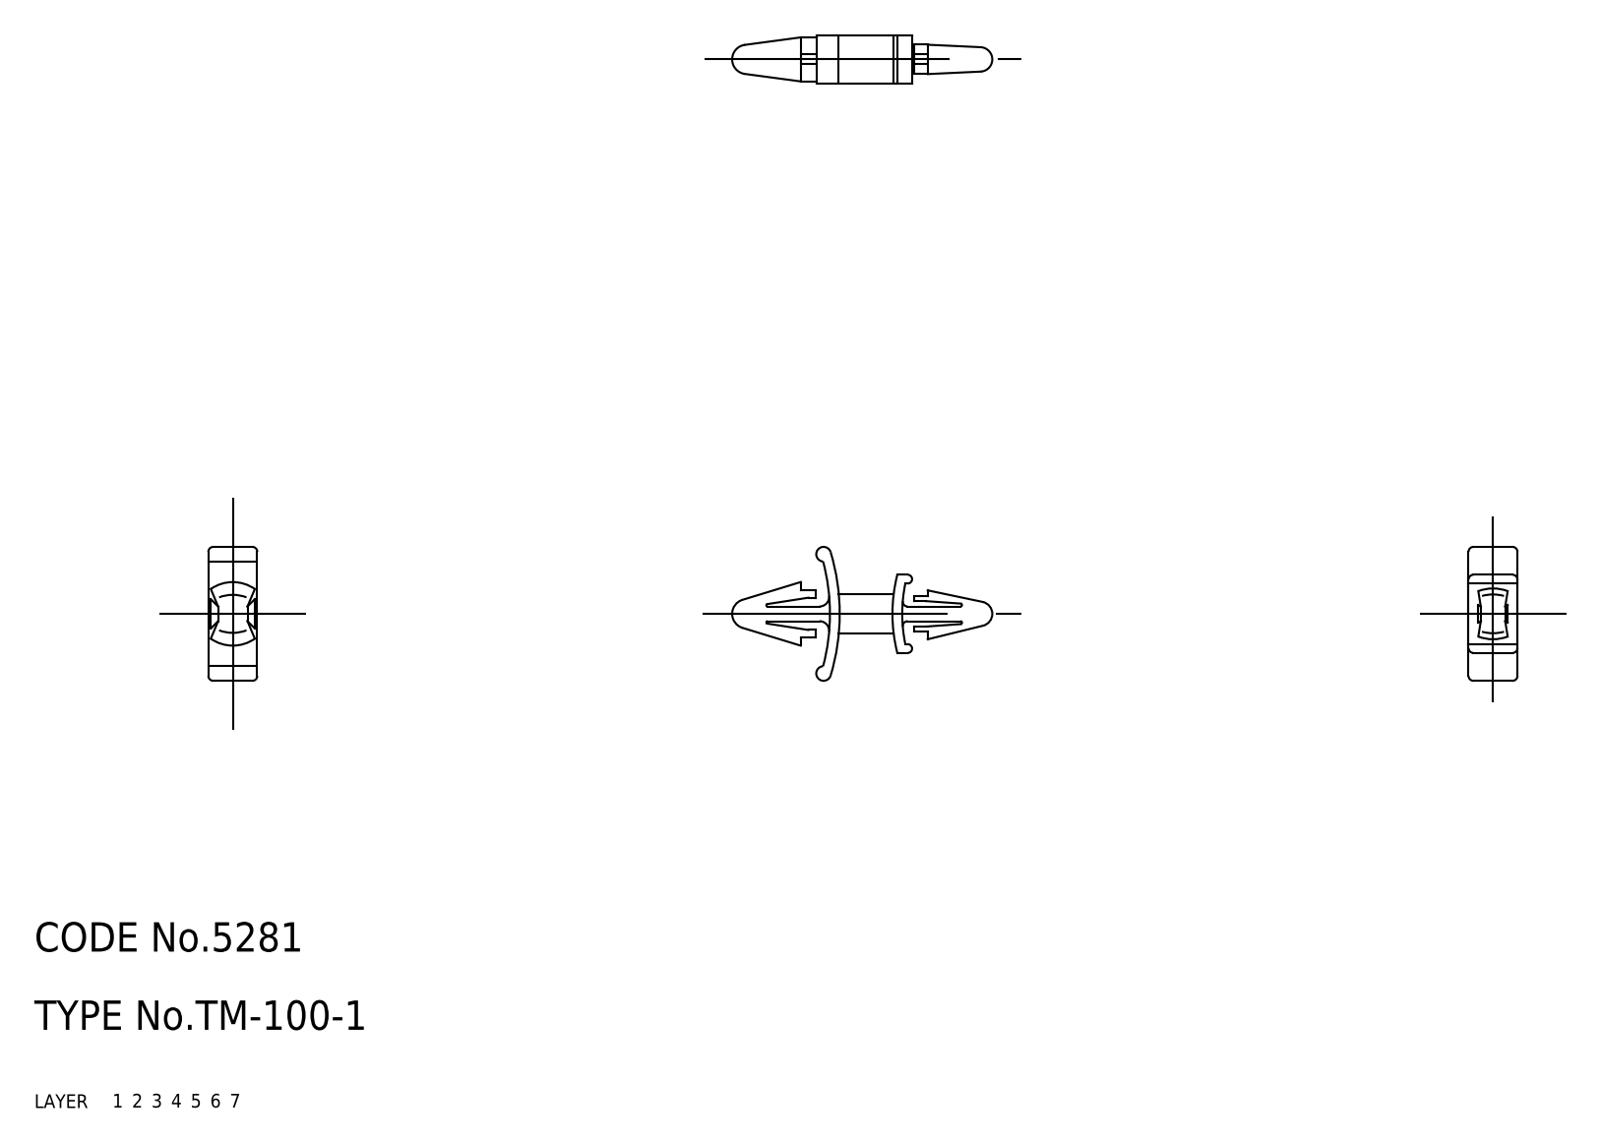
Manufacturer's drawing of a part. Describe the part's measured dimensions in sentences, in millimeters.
The part is named "holder". Its 3-D file was written by "CADfix (AUTOMOTIVE_DESIGN)". It is 1 solid with 78 faces: 0 planar, 0 cylindrical and 78 other. Overall it measures 26.6 by 13.7 by 5 millimeters. Its volume is 398 cubic millimeters and its surface area 694 square millimeters.
